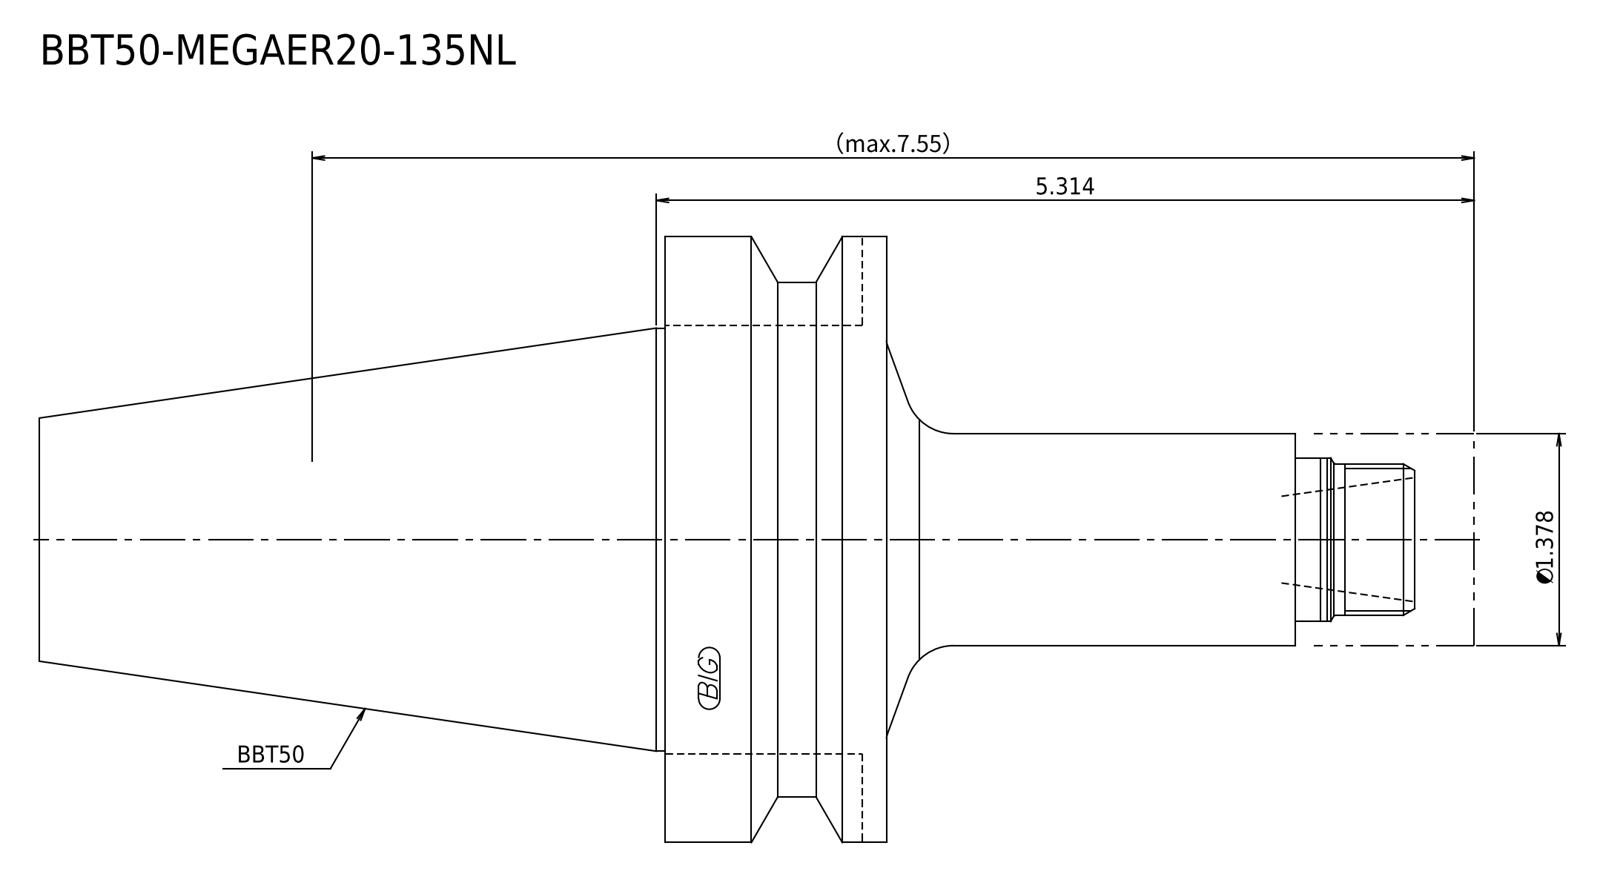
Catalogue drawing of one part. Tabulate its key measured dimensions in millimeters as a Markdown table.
| quantity | value |
| --- | --- |
| STEP written by | Kubotek KeyCreator 2011 V10.0.2 (22737) (automotive_design) |
| units | millimeters |
| bodies | 2 solids, 21 faces (7 planar, 8 cylindrical, 6 other) |
| overall size | 236.8 × 100 × 100 |
| volume | 629 288 mm³ |
| surface area | 57 822 mm² |
| round bosses / shafts (diameter × count) | 100 × 1, 85 × 1, 69.85 × 1, 35 × 1, 27 × 1, 25 × 1 |
| main face-to-face distances | 36.5, 139.8, 103.3, 70.5, 107, 210.3, 26.5, 97, 133.5, 236.8 |
